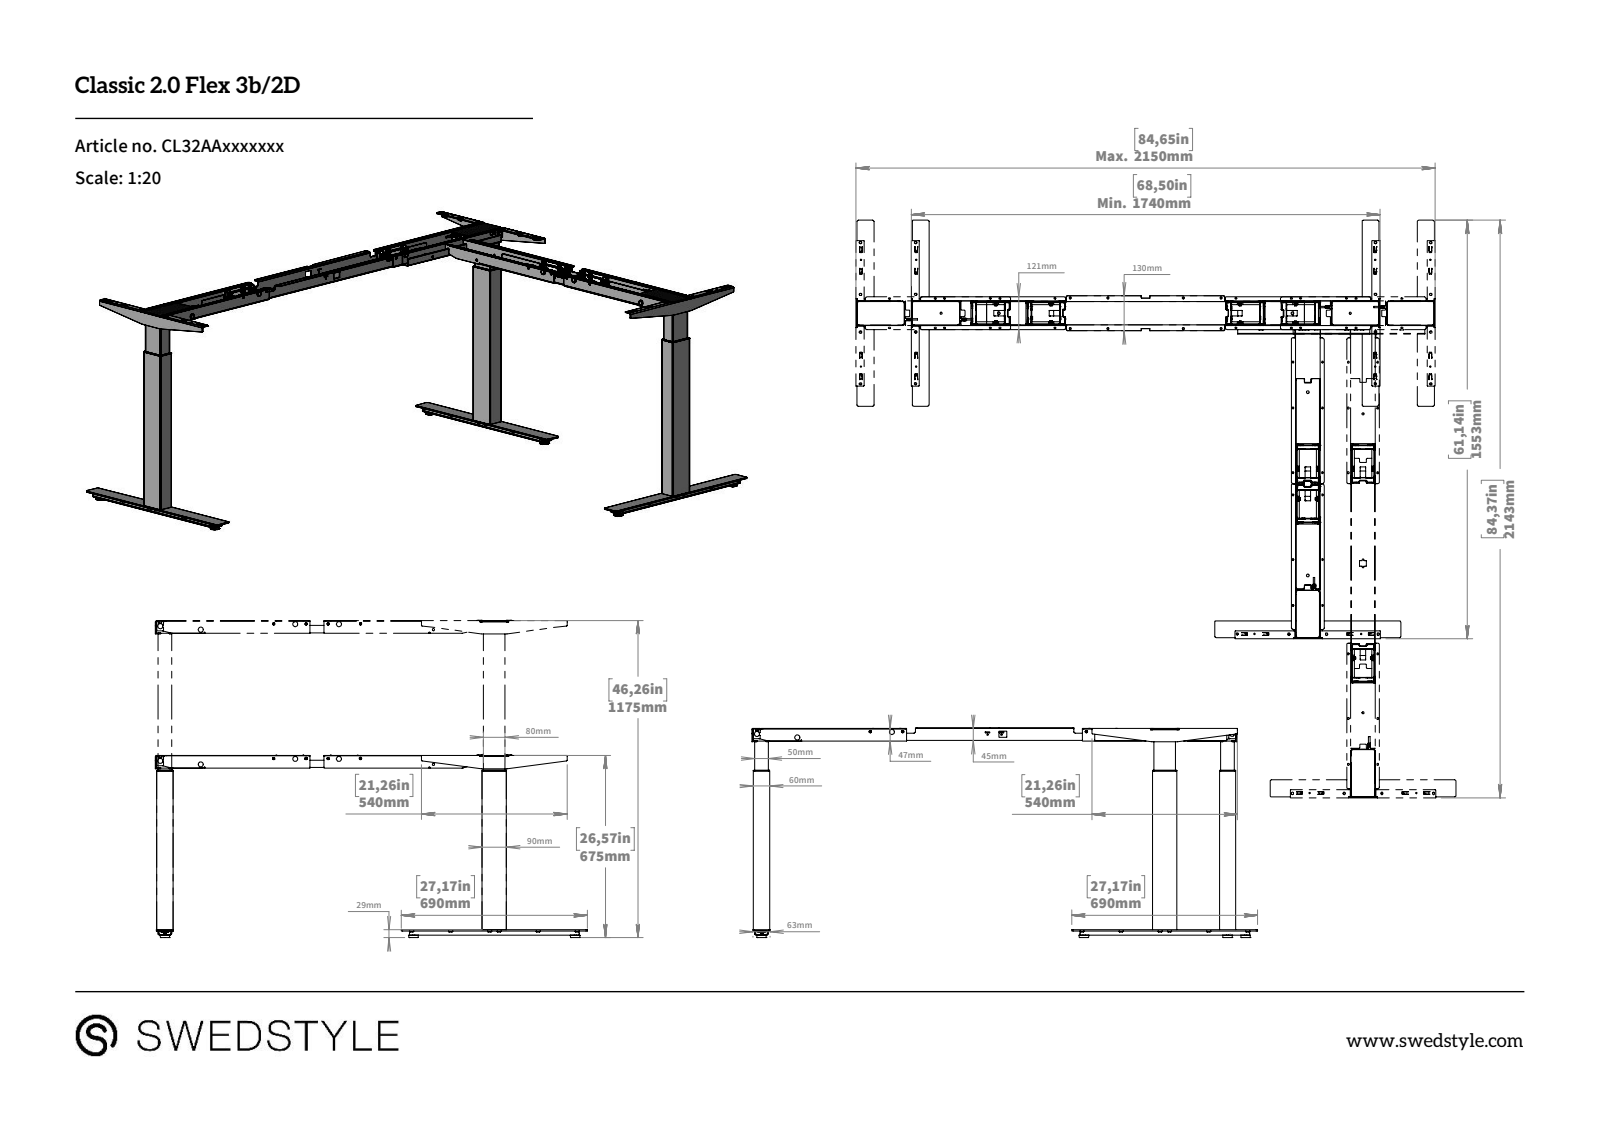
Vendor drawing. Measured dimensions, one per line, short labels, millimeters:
name: CL32AAxxxxxxx_Fl174_Fl115
written by: SolidWorks 2015 (CONFIG_CONTROL_DESIGN)
unit: mm
bodies: 0 solids, 2038 faces (1065 planar, 713 cylindrical, 260 other)
size: 1877 × 1602.88 × 726.9
holes: 12× ⌀16, 11× ⌀6, 7× ⌀8, 6× ⌀5, 6× ⌀14, 4× ⌀7, 3× ⌀10, 1× ⌀5.4, 1× ⌀8.5
bosses: 3× ⌀8.5, 3× ⌀5.5, 1× ⌀15.57, 1× ⌀8
rounds: 133× R0.5, 54× R2.5, 47× R2, 36× R3, 35× R1, 34× R4, 30× R2.75, 23× R5
face distances: 2, 2.5, 4, 90.5, 0.5, 654.3, 60, 92.5, 93, 90
hole spacings: 140, 180.54, 280, 302.32, 114, 203.3, 237.26, 357.37
